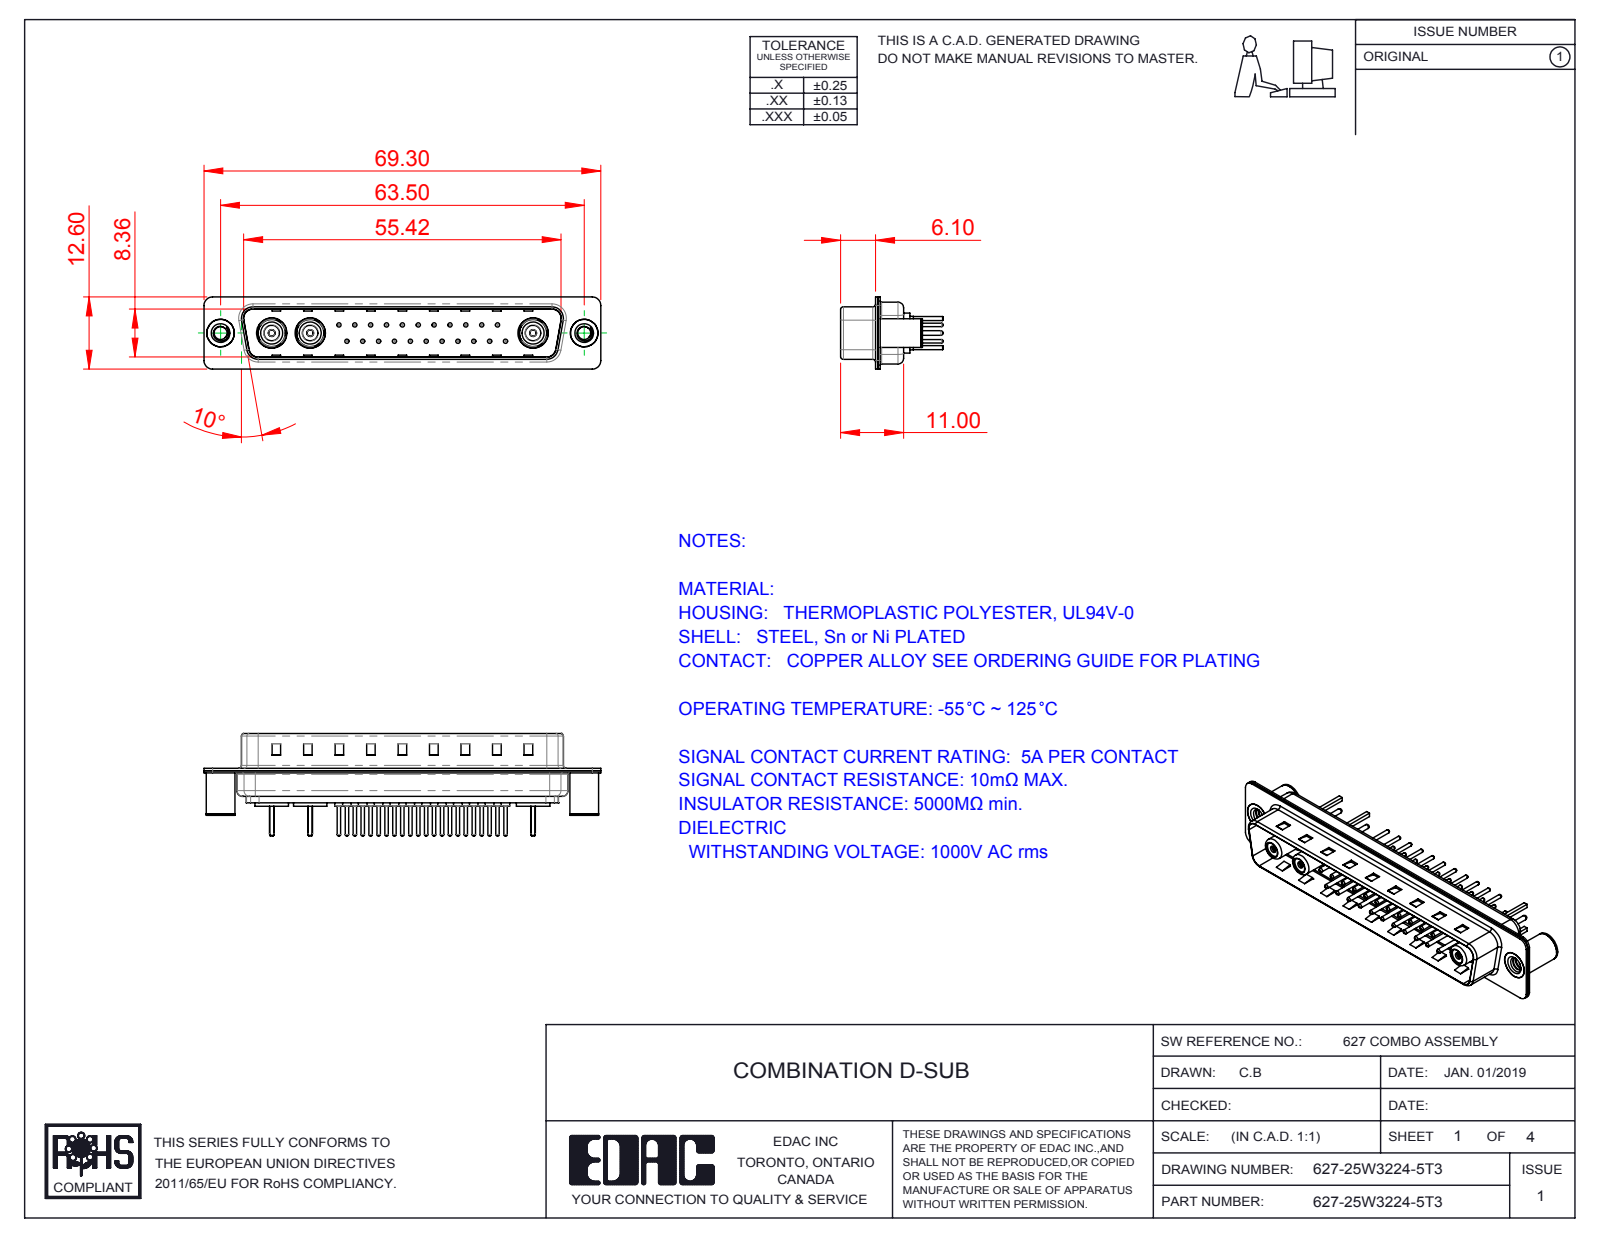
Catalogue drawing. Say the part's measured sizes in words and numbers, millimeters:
The part is named "627Combo Threaded Board Spacer_3; Co-Ax Jack_Straight PC Tail; Co-Ax Jack Assy_S; Socket_Str (+8 more)". Its 3-D file was written by "SolidWorks 2016 (CONFIG_CONTROL_DESIGN)". It is 42 solids with 1593 faces: 498 planar, 614 cylindrical and 481 other. Overall it measures 69.3 by 17.9 by 12.6 millimeters. Its volume is 3 955 cubic millimeters and its surface area 10 654 square millimeters. Round holes: 25 of diameter 1.6, 22 of diameter 0.75, 22 of diameter 2, 3 of diameter 1.1, 3 of diameter 1.2, 3 of diameter 1.5, 3 of diameter 2.5, 3 of diameter 2.7, 3 of diameter 3.4, 3 of diameter 4.85, 3 of diameter 5.3, 2 of diameter 2.26. Round bosses or shafts: 22 of diameter 1.5, 22 of diameter 0.6, 3 of diameter 5.85, 3 of diameter 5.2, 3 of diameter 4.8, 3 of diameter 4.73, 3 of diameter 3.85, 3 of diameter 3.75. Partial cylindrical surfaces (rounded edges, fillets, slot ends): 16 of radius 1.5, 12 of radius 2, 8 of radius 0.5, 8 of radius 1.6, 4 of radius 0.25, 4 of radius 0.6, 4 of radius 0.65, 4 of radius 0.9. The main face-to-face distances are 0.4, 0.82, 9.58, 8.76, 1.5, 1.22, 5.6, 0.42, 9.98, 9.18. The hole center spacings are 3.16, 2.77, 5.54, 8.31, 5.03, 5.04, 7.49, 11.08.
